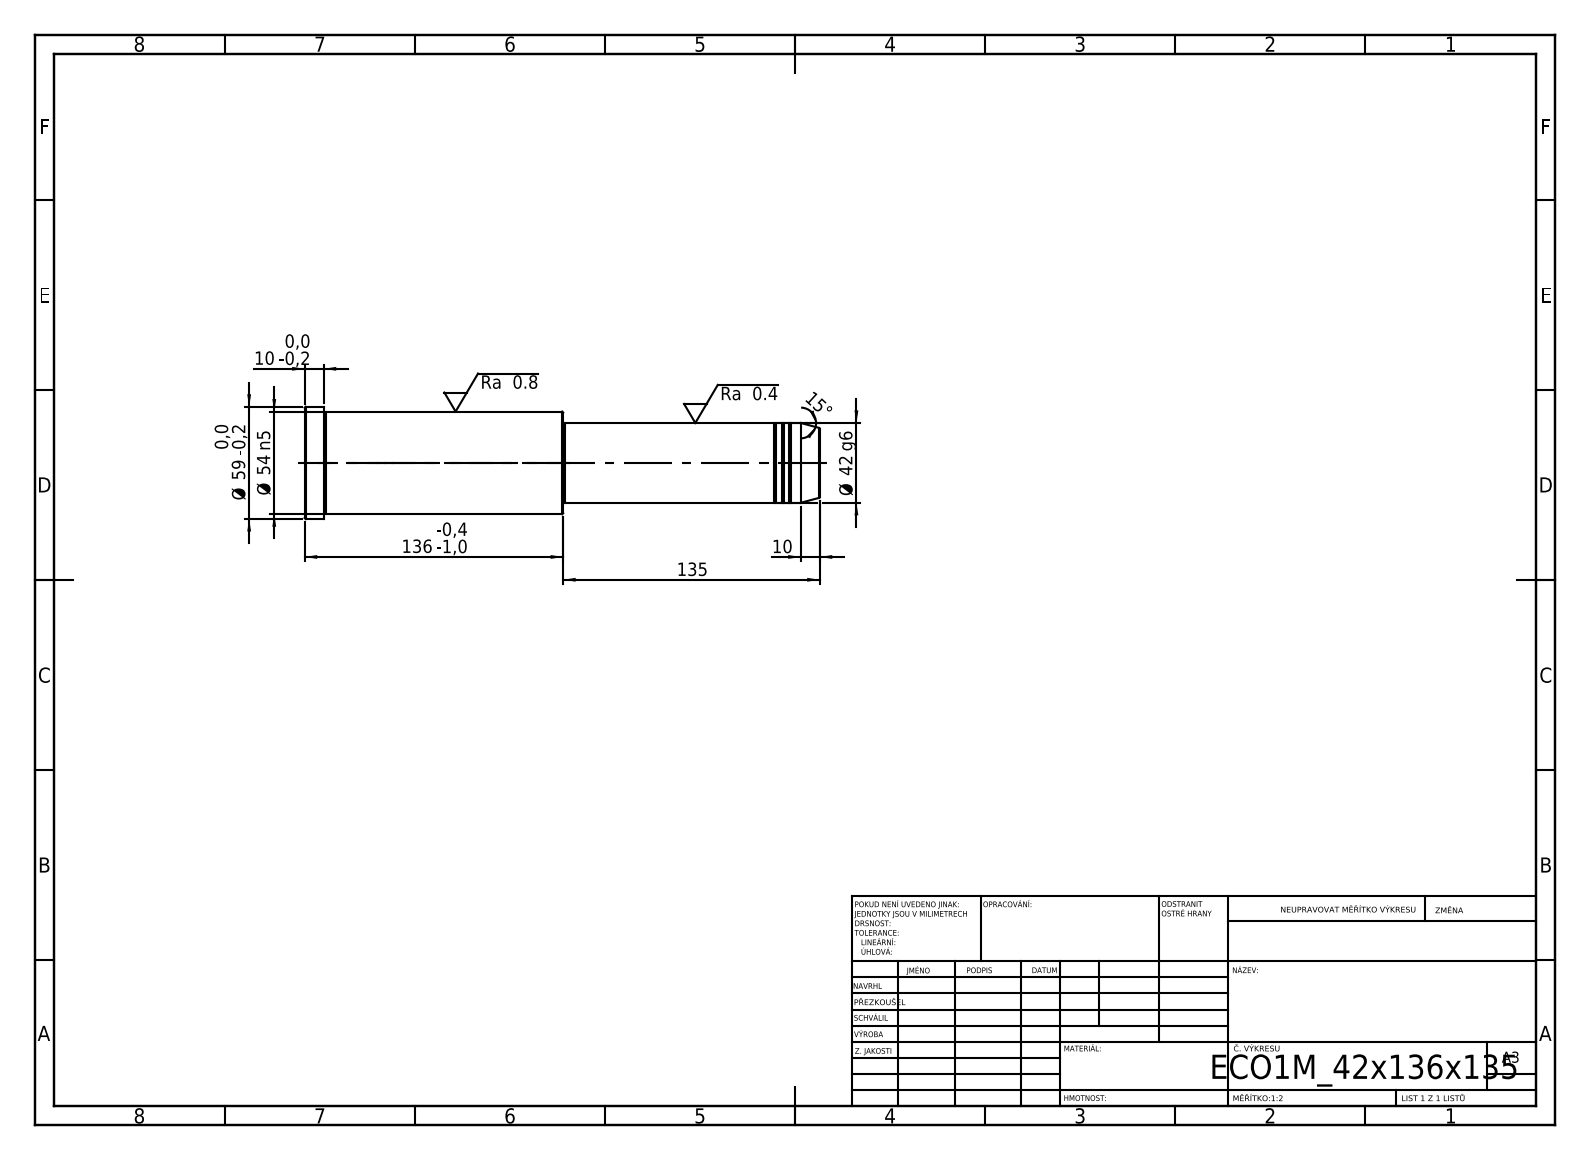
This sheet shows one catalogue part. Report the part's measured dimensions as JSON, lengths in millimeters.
{"step_written_by": "SolidWorks 2019 (CONFIG_CONTROL_DESIGN)", "units": "millimeters", "bodies": {"solids": 1, "faces": 43, "planar": 5, "cylindrical": 14, "other": 24}, "overall_size": [271, 59, 59], "volume_mm3": 500917, "surface_area_mm2": 46458, "round_bosses_or_shafts": [[59, 1], [54, 1], [42, 1], [41, 1]], "face_to_face_distances": [271, 135, 136, 261, 126, 10, 134, 1, 127, 137]}
